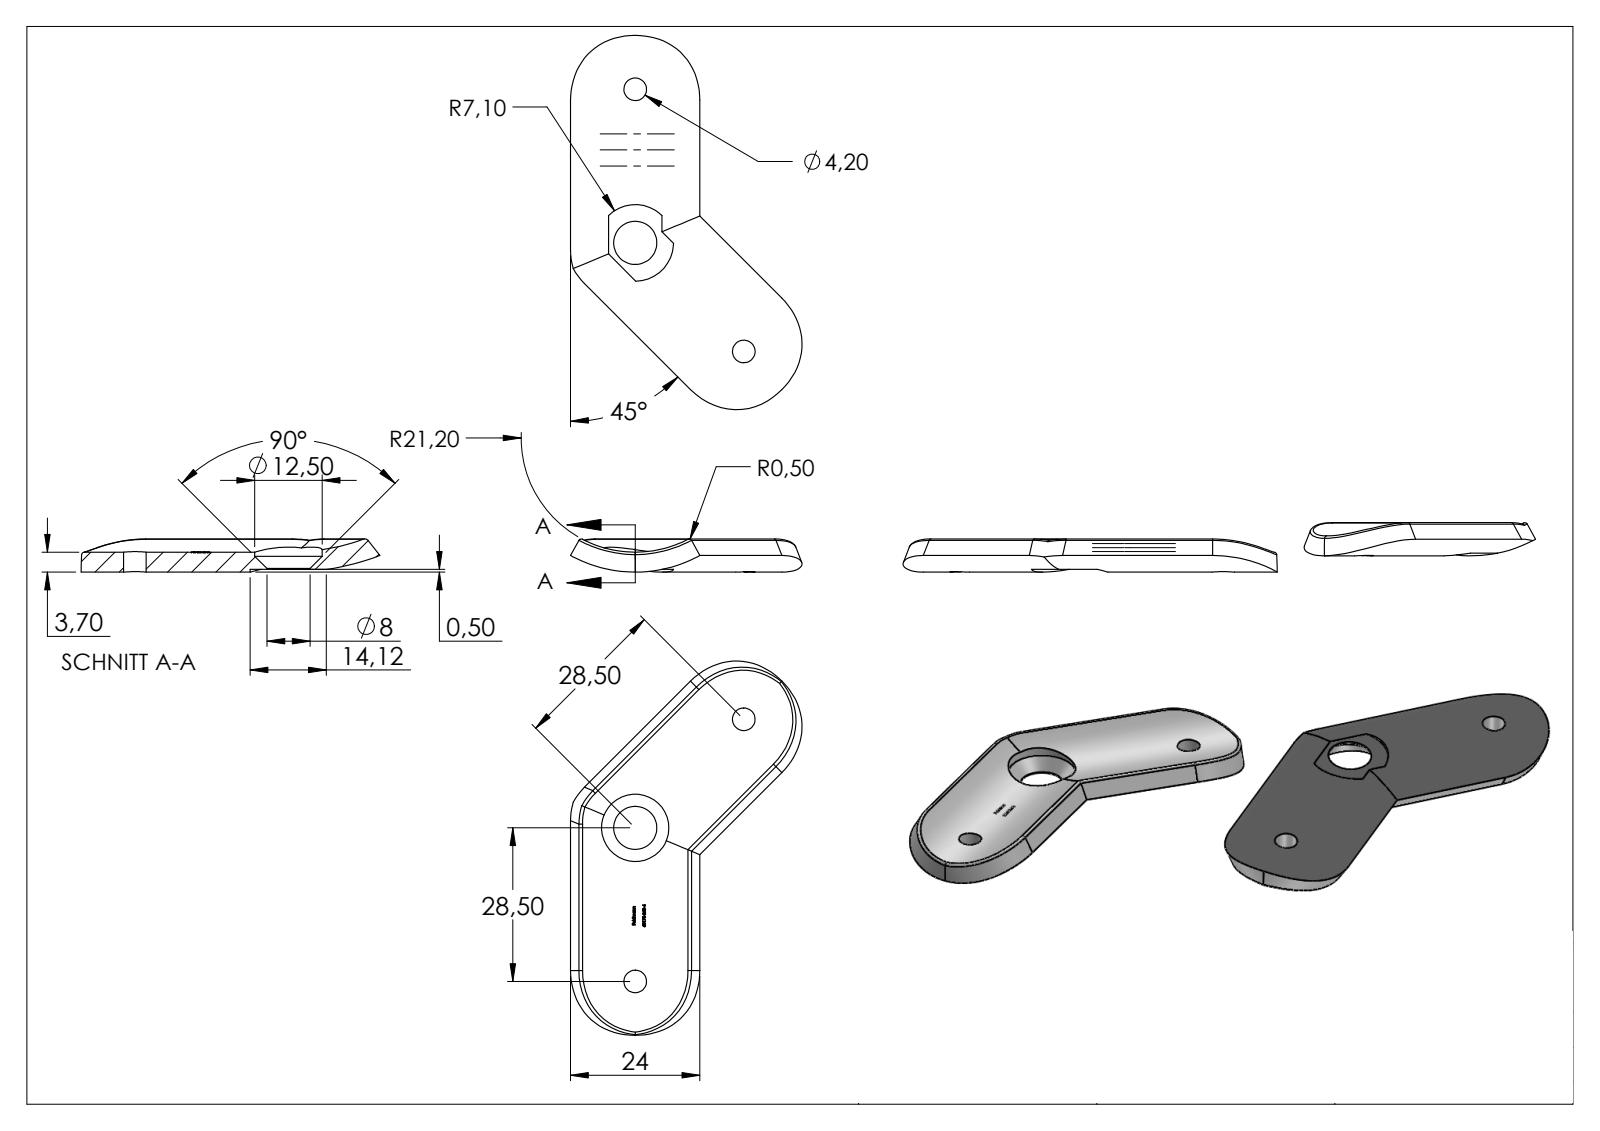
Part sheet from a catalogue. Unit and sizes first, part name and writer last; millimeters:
Units: millimetres
Overall size (bounding box): 69.47 × 42.97 × 6.15
Round holes (diameter × count): ⌀4.2 ×2, ⌀8 ×1, ⌀12.5 ×1
Partial cylindrical surfaces — rounded edges, fillets, slot ends (radius × count): R0.5 ×4, R12 ×4, R21.2 ×2, R24.9 ×2, R7.1 ×1, R10 ×1, R21.3 ×1
Main face-to-face distances: 1.96, 0.55, 0.5, 1.74, 1.9, 1.79, 0.68, 0.87, 1.84, 1.78
Hole centre spacings: 28.5, 52.66
Volume: 5 661 mm³ · Surface area: 3 981 mm²
Bodies: 1 solid, 273 faces (114 planar, 53 cylindrical, 106 other)
Part name (STEP PRODUCT): 60178-240-4
STEP written by: SolidWorks 2015 (CONFIG_CONTROL_DESIGN)
